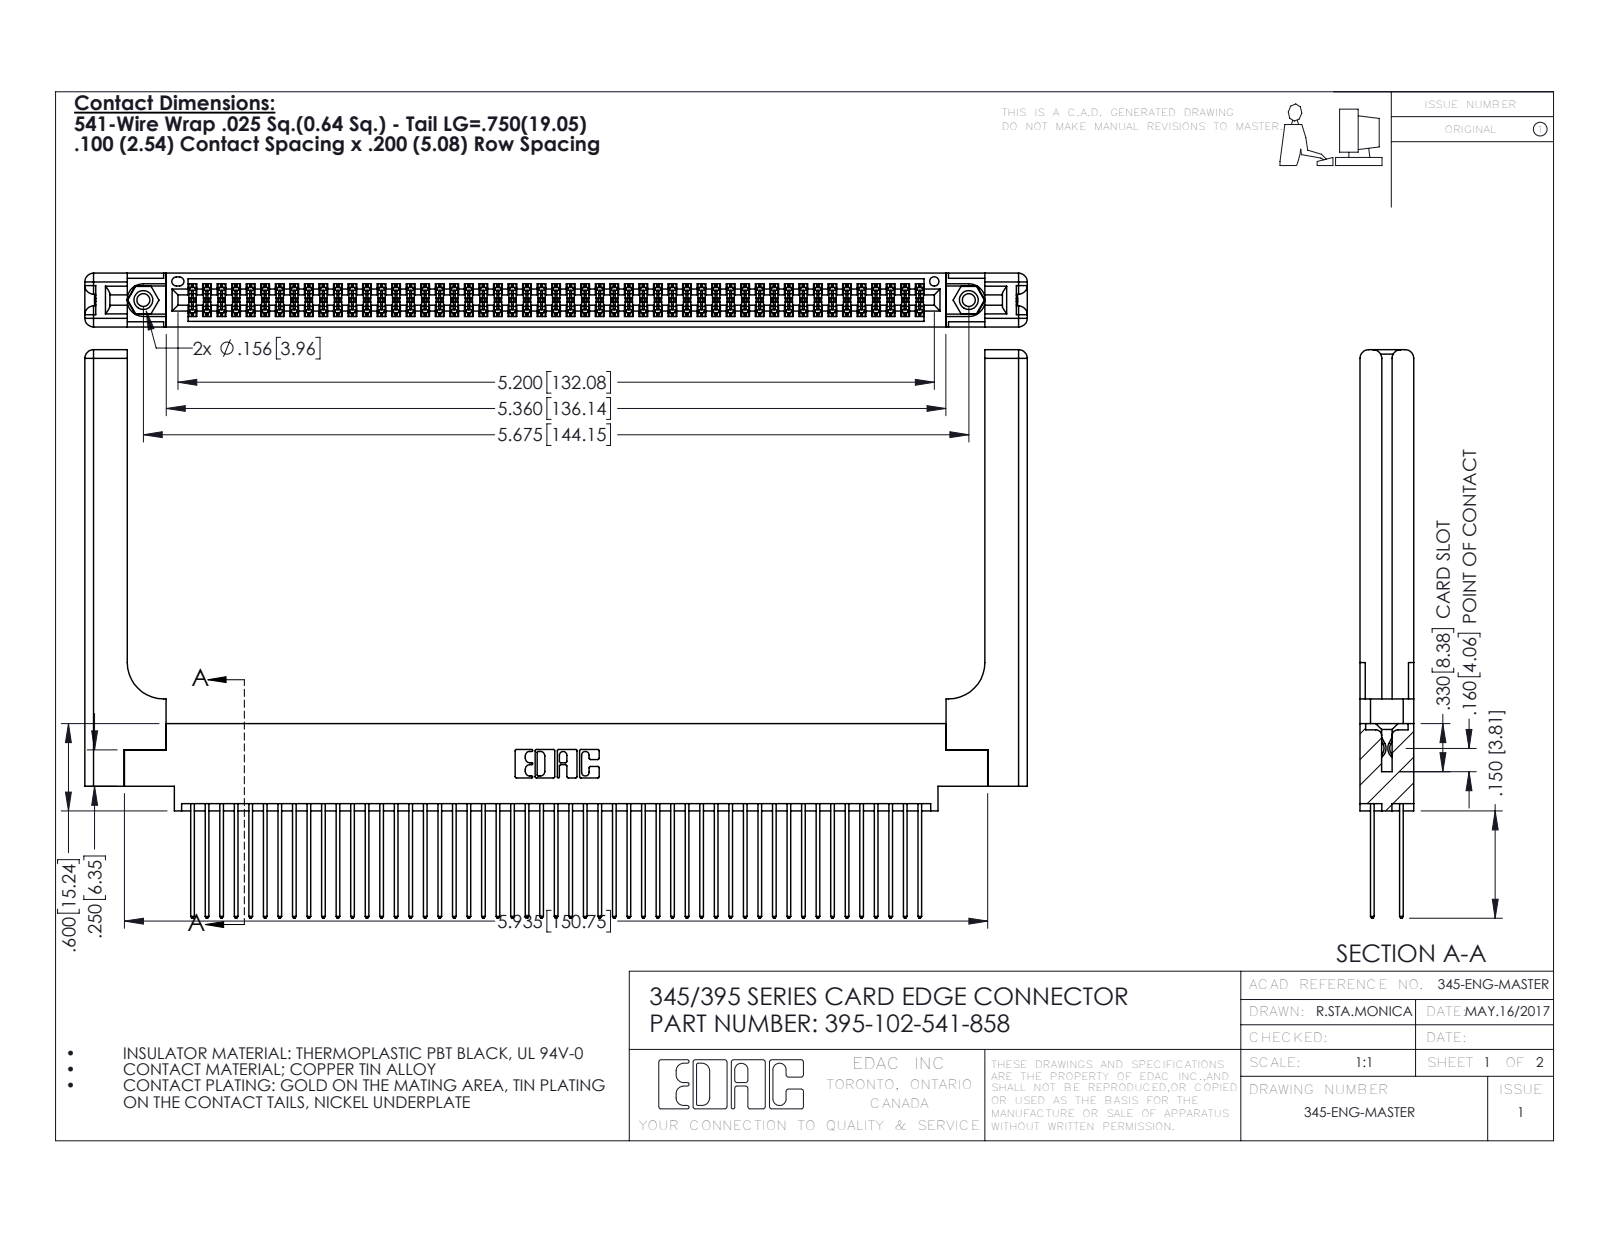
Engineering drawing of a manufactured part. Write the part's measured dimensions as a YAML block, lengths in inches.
part_name: "345-292-001_345-293-141; 345 Part_0.170 Offset - 0.156 Dia-TH; 345-250-001_345-250-001-102; 395-102-541-858 (+1 more)"
step_written_by: "SolidWorks 2016 (CONFIG_CONTROL_DESIGN)"
units: inches
bodies: {solids: 107, faces: 5486, planar: 3598, cylindrical: 1828, other: 60}
overall_size: [6.479, 3.907, 0.37]
volume: 1.527
surface_area: 50.5
round_holes:
  - {diameter: 0.089, count: 2}
  - {diameter: 0.125, count: 2}
  - {diameter: 0.156, count: 2}
  - {diameter: 0.064, count: 1}
round_bosses_or_shafts:
  - {diameter: 0.155, count: 2}
partial_cylinders:
  - {radius: 0.006, count: 153}
  - {radius: 0.01, count: 102}
  - {radius: 0.01, count: 22}
  - {radius: 0.06, count: 16}
  - {radius: 0.007, count: 6}
  - {radius: 0.031, count: 6}
  - {radius: 0.026, count: 3}
  - {radius: 0.014, count: 2}
face_to_face_distances: [0.072, 0.298, 0.37, 0.098, 0.272, 0.025, 0.2, 0.225, 0.175, 0.148]
hole_center_spacings: [0.27, 5.439, 5.675]
